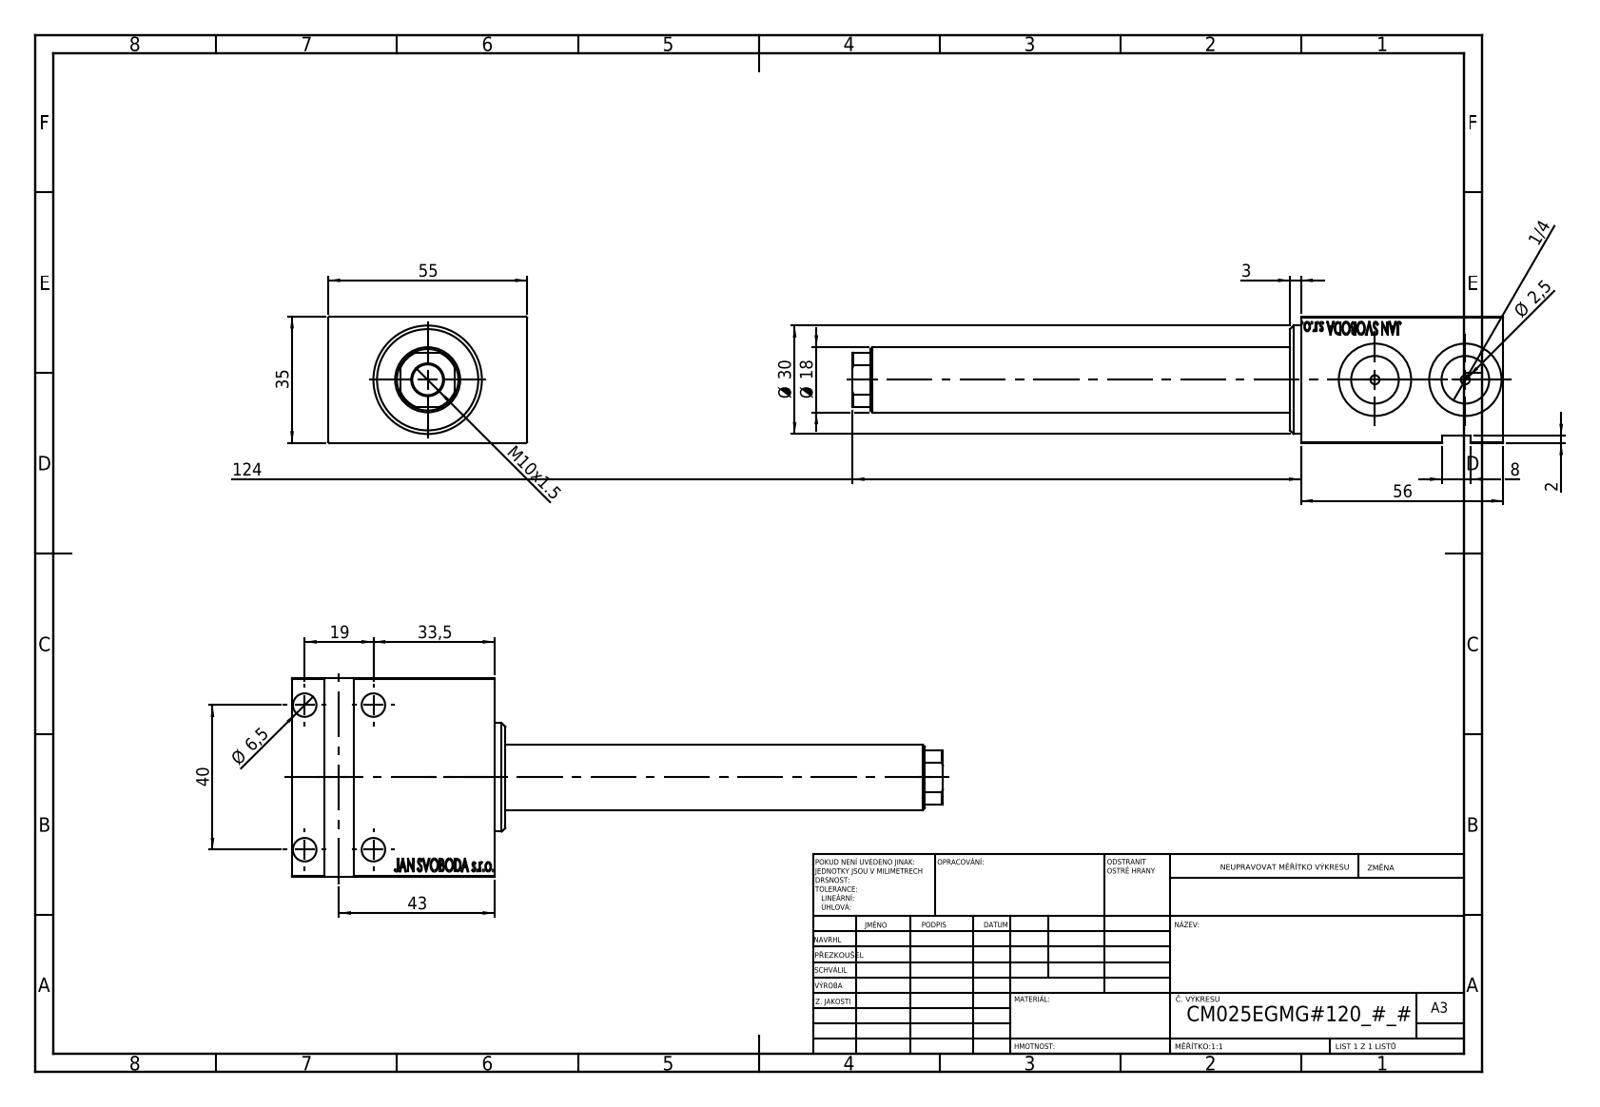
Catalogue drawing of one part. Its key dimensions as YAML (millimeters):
part_name: "V450CM_E_Body; V450CM_E_VCP; V450CM_VC_B"
step_written_by: "SolidWorks 2019 (CONFIG_CONTROL_DESIGN)"
units: millimeters
bodies: {solids: 3, faces: 849, planar: 407, cylindrical: 48, other: 394}
overall_size: [180, 55, 35]
volume: 129503
surface_area: 37503
round_holes:
  - {diameter: 6.5, count: 4}
  - {diameter: 2.5, count: 2}
  - {diameter: 10.5, count: 2}
  - {diameter: 13.16, count: 2}
  - {diameter: 20, count: 2}
  - {diameter: 8.5, count: 1}
  - {diameter: 18, count: 1}
  - {diameter: 25, count: 1}
round_bosses_or_shafts:
  - {diameter: 30, count: 1}
  - {diameter: 27, count: 1}
partial_cylinders:
  - {radius: 5.25, count: 2}
  - {radius: 8.5, count: 1}
face_to_face_distances: [35, 56, 55, 5, 51, 33, 2, 42, 3, 59]
hole_center_spacings: [19, 40, 44.28, 25]
